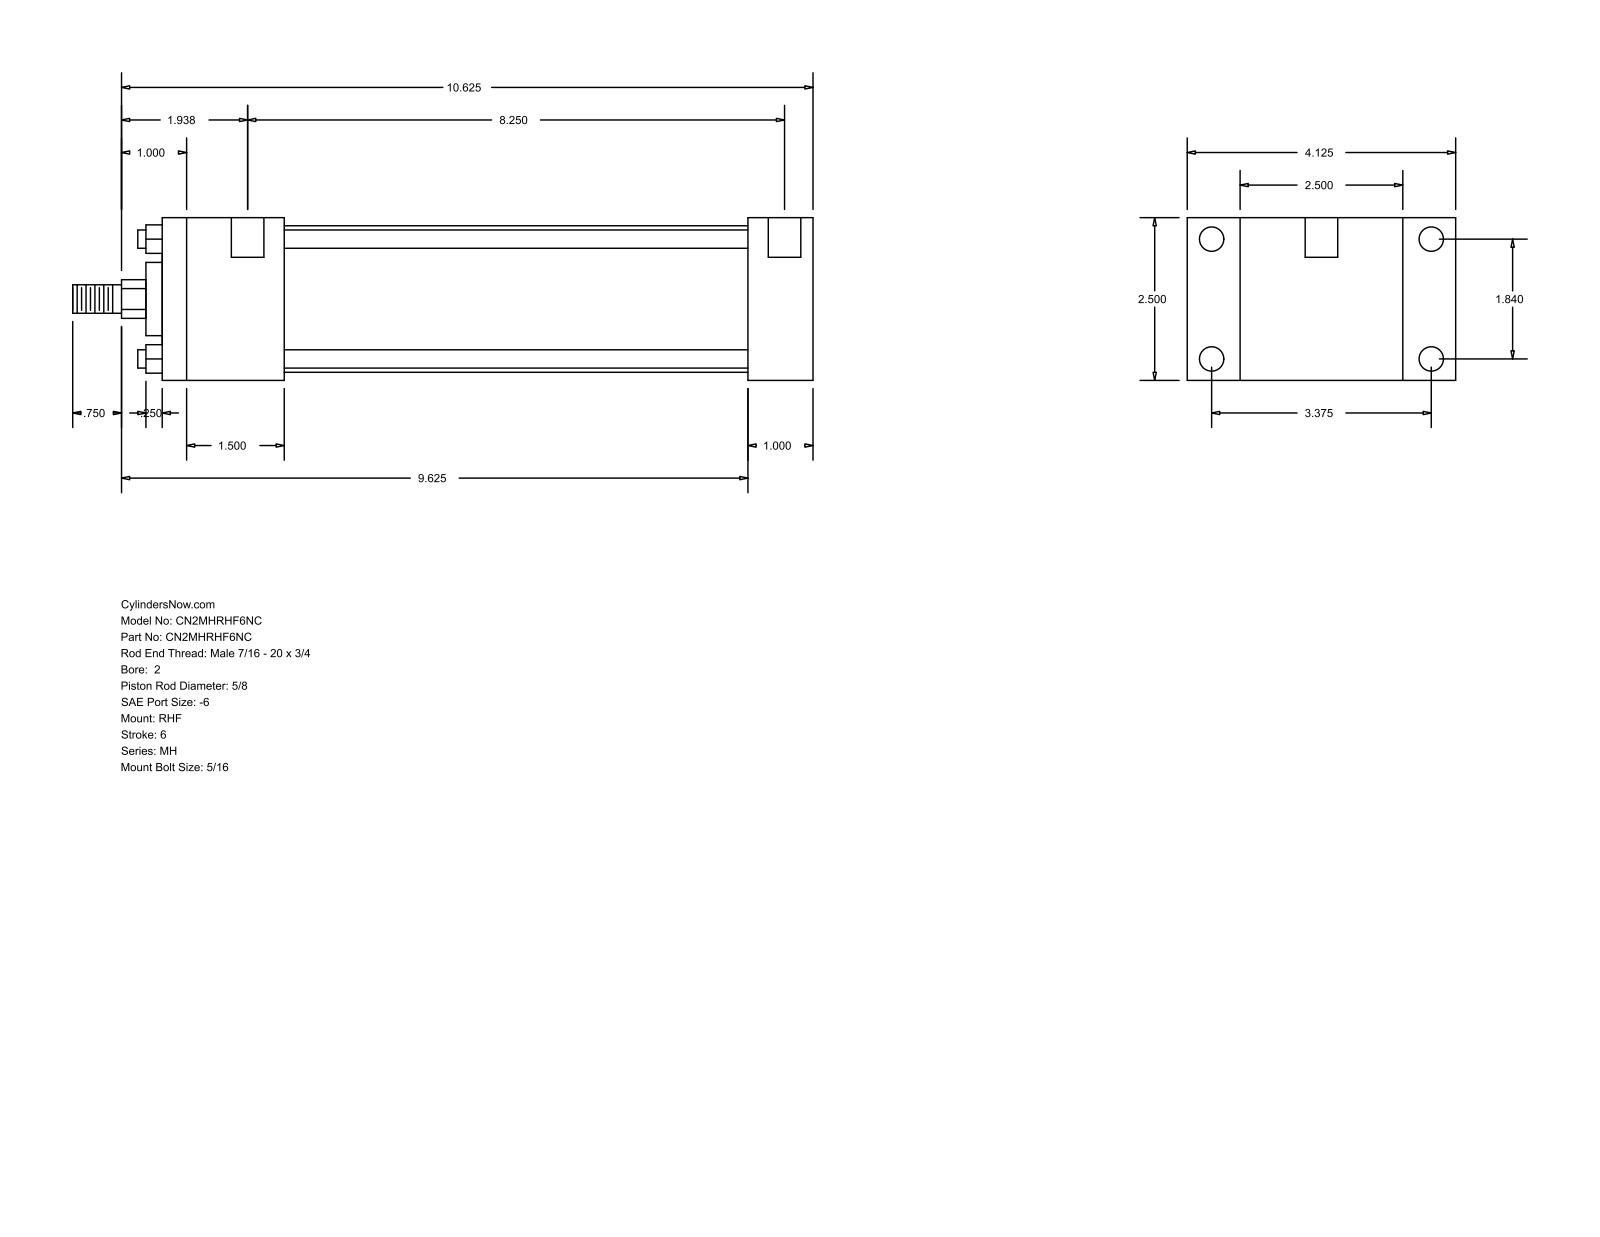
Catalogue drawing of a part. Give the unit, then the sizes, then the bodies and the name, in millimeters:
Units: millimetres
Overall size (bounding box): 288.93 × 104.78 × 63.5
Round holes (diameter × count): ⌀5.56 ×4, ⌀9.53 ×4, ⌀12.7 ×2
Round bosses / shafts (diameter × count): ⌀7.14 ×4, ⌀57.15 ×1, ⌀28.57 ×1, ⌀15.88 ×1, ⌀11.11 ×1
Partial cylindrical surfaces — rounded edges, fillets, slot ends (radius × count): R7.54 ×1
Main face-to-face distances: 63.5, 25.41, 20.64, 84.14, 228.59, 254, 104.78, 47.62, 180.97, 206.38
Hole centre spacings: 46.74, 85.72, 97.63, 217.49, 3.18, 4.76, 209.55, 212.73
Bodies: 0 solids, 88 faces (60 planar, 28 cylindrical, 0 other)
Part name (STEP PRODUCT): MH_RHF__0200_0.625
STEP written by: GSSL Pune (CONFIG_CONTROL_DESIGN)
